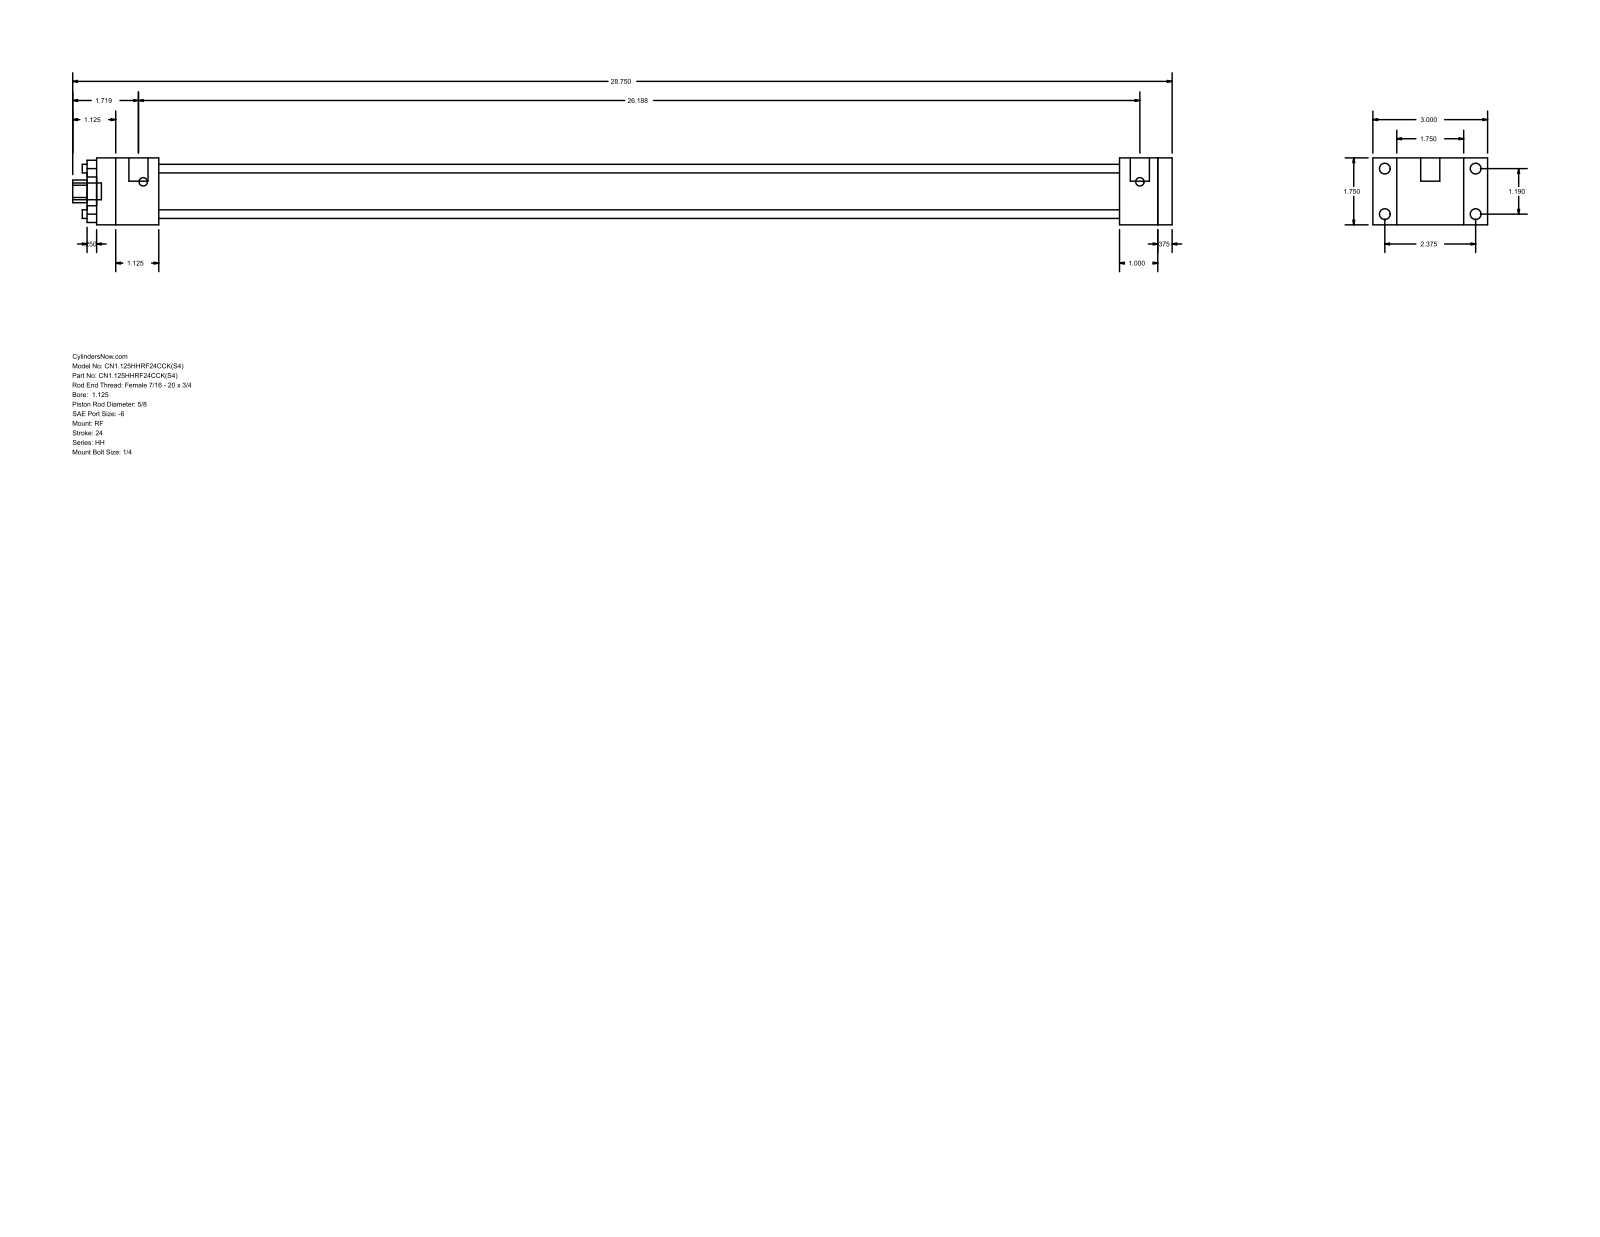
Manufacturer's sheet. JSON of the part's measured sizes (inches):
{"part_name": "HH_RF__0112_0.625", "step_written_by": "GSSL Pune (CONFIG_CONTROL_DESIGN)", "units": "inches", "bodies": {"solids": 0, "faces": 92, "planar": 64, "cylindrical": 28, "other": 0}, "overall_size": [28.75, 3, 1.75], "round_holes": [[0.225, 4], [0.625, 1], [1.125, 1], [1.375, 1]], "round_bosses_or_shafts": [[0.281, 4], [0.219, 4], [0.5, 2], [0.437, 1]], "partial_cylinders_radius": [[0.297, 1]], "face_to_face_distances": [1.75, 0.375, 0.625, 26.125, 26.5, 25.125, 1, 1.375, 1.625, 26.75], "hole_center_spacings": [0.841, 1.19, 1.683]}
